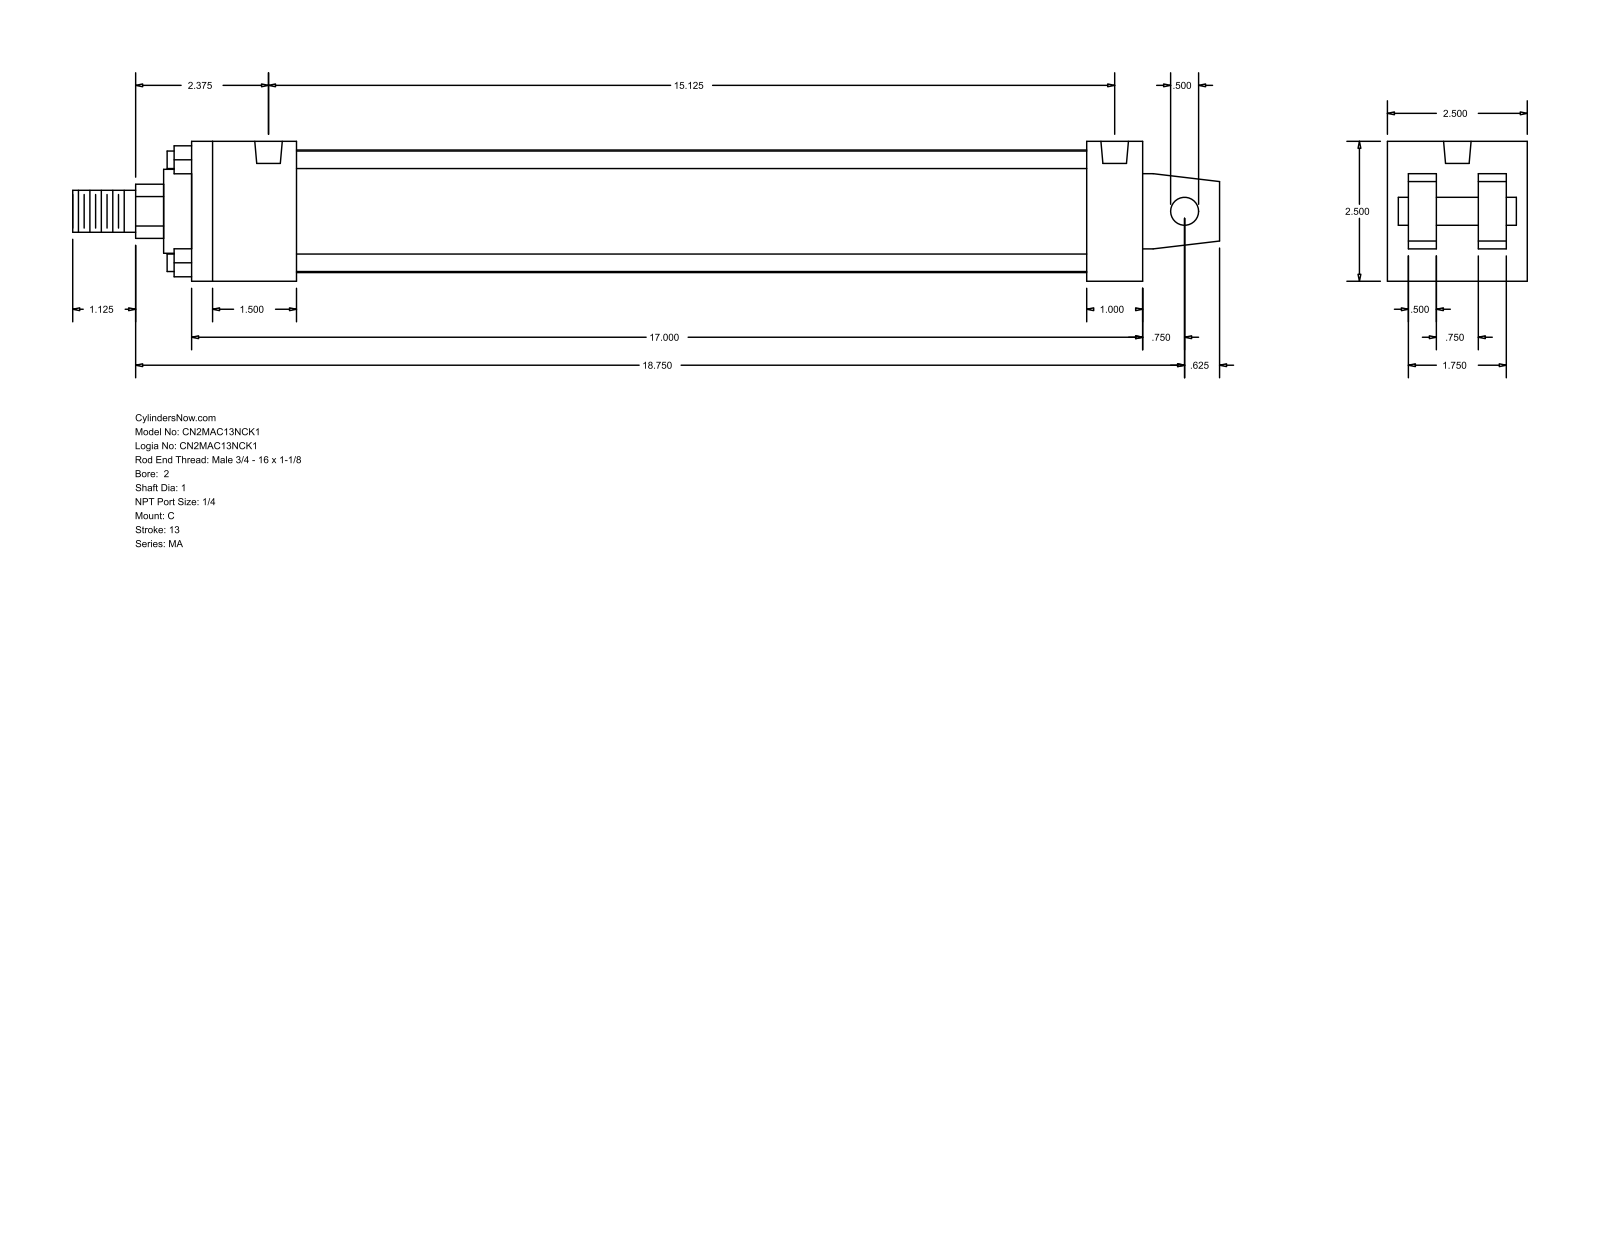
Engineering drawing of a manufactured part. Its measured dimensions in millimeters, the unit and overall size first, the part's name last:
Units: millimetres
Overall size (bounding box): 520.7 × 63.5 × 63.5
Round holes (diameter × count): ⌀7.94 ×4, ⌀12.49 ×2
Round bosses / shafts (diameter × count): ⌀7.94 ×4, ⌀55.63 ×1, ⌀38.1 ×1, ⌀25.4 ×1, ⌀19.05 ×1, ⌀12.7 ×1
Partial cylindrical surfaces — rounded edges, fillets, slot ends (radius × count): R12.29 ×1
Main face-to-face distances: 63.5, 12.7, 431.8, 22.22, 41.28, 9.52, 53.98, 31.76, 47.63, 25.4
Hole centre spacings: 384.17
Bodies: 0 solids, 103 faces (76 planar, 27 cylindrical, 0 other)
Part name (STEP PRODUCT): MA_C__0200_1
STEP written by: GSSL Pune (CONFIG_CONTROL_DESIGN)
